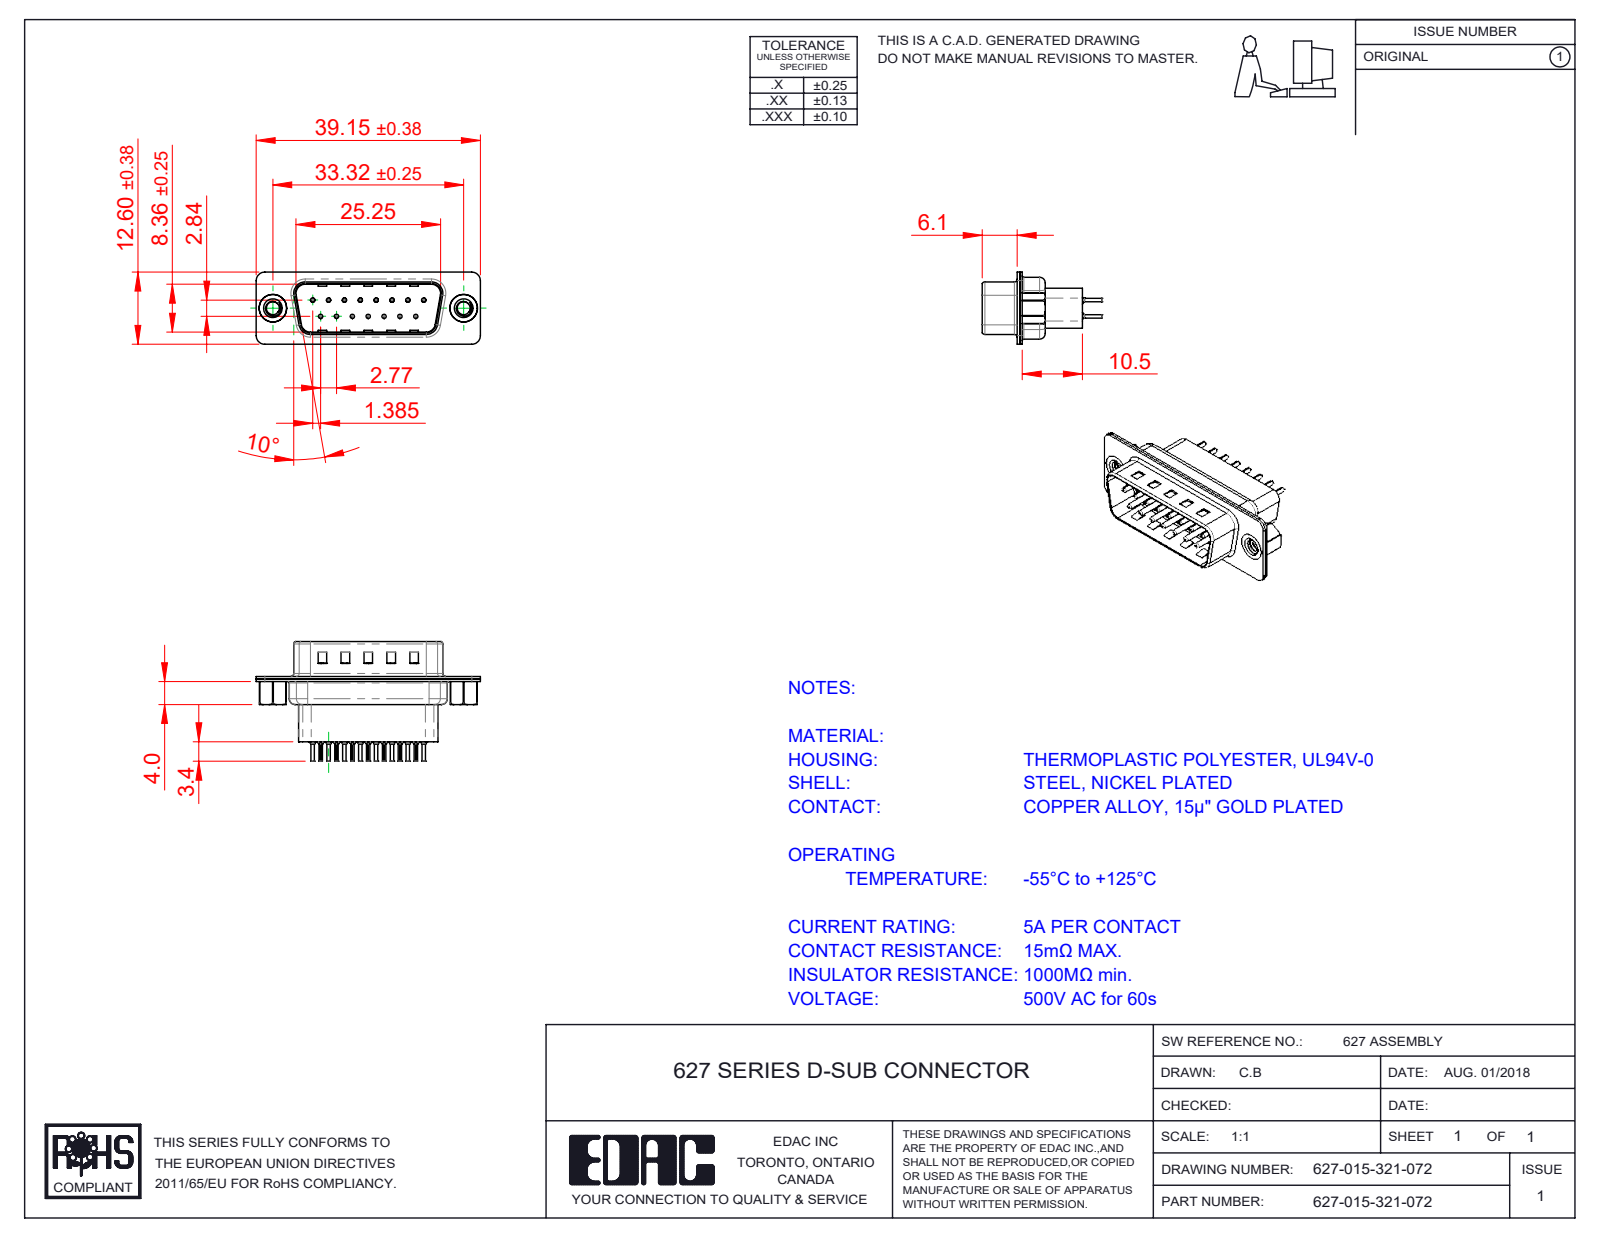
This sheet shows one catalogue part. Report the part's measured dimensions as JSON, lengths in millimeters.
{"part_name": "627 Housing_15 HP; 627-015-321-072; 627 Shell Front_15 Contacts; 627 Contact Row 1_21H (+3 more)", "step_written_by": "SolidWorks 2020 (CONFIG_CONTROL_DESIGN)", "units": "millimeters", "bodies": {"solids": 20, "faces": 1806, "planar": 499, "cylindrical": 686, "other": 621}, "overall_size": [39.15, 20.8, 12.6], "volume_mm3": 2534, "surface_area_mm2": 6600, "round_holes": [[0.2, 15], [0.35, 15], [1.1, 15], [1.6, 15], [2.26, 2], [4, 2], [4.8, 2]], "round_bosses_or_shafts": [[2, 15], [1.5, 15], [0.75, 15], [0.6, 15], [5, 2], [4.9, 2]], "partial_cylinders_radius": [[0.1, 30], [1.5, 16], [2, 12], [0.5, 8], [1.6, 8], [0.25, 4], [0.6, 4], [0.65, 4]], "face_to_face_distances": [0.4, 0.45, 0.9, 0.82, 9.58, 1.5, 0.68, 7.68, 1.4, 1.08], "hole_center_spacings": [3.16, 2.77, 5.54, 8.31, 11.08, 5.03, 5.04, 7.48]}
